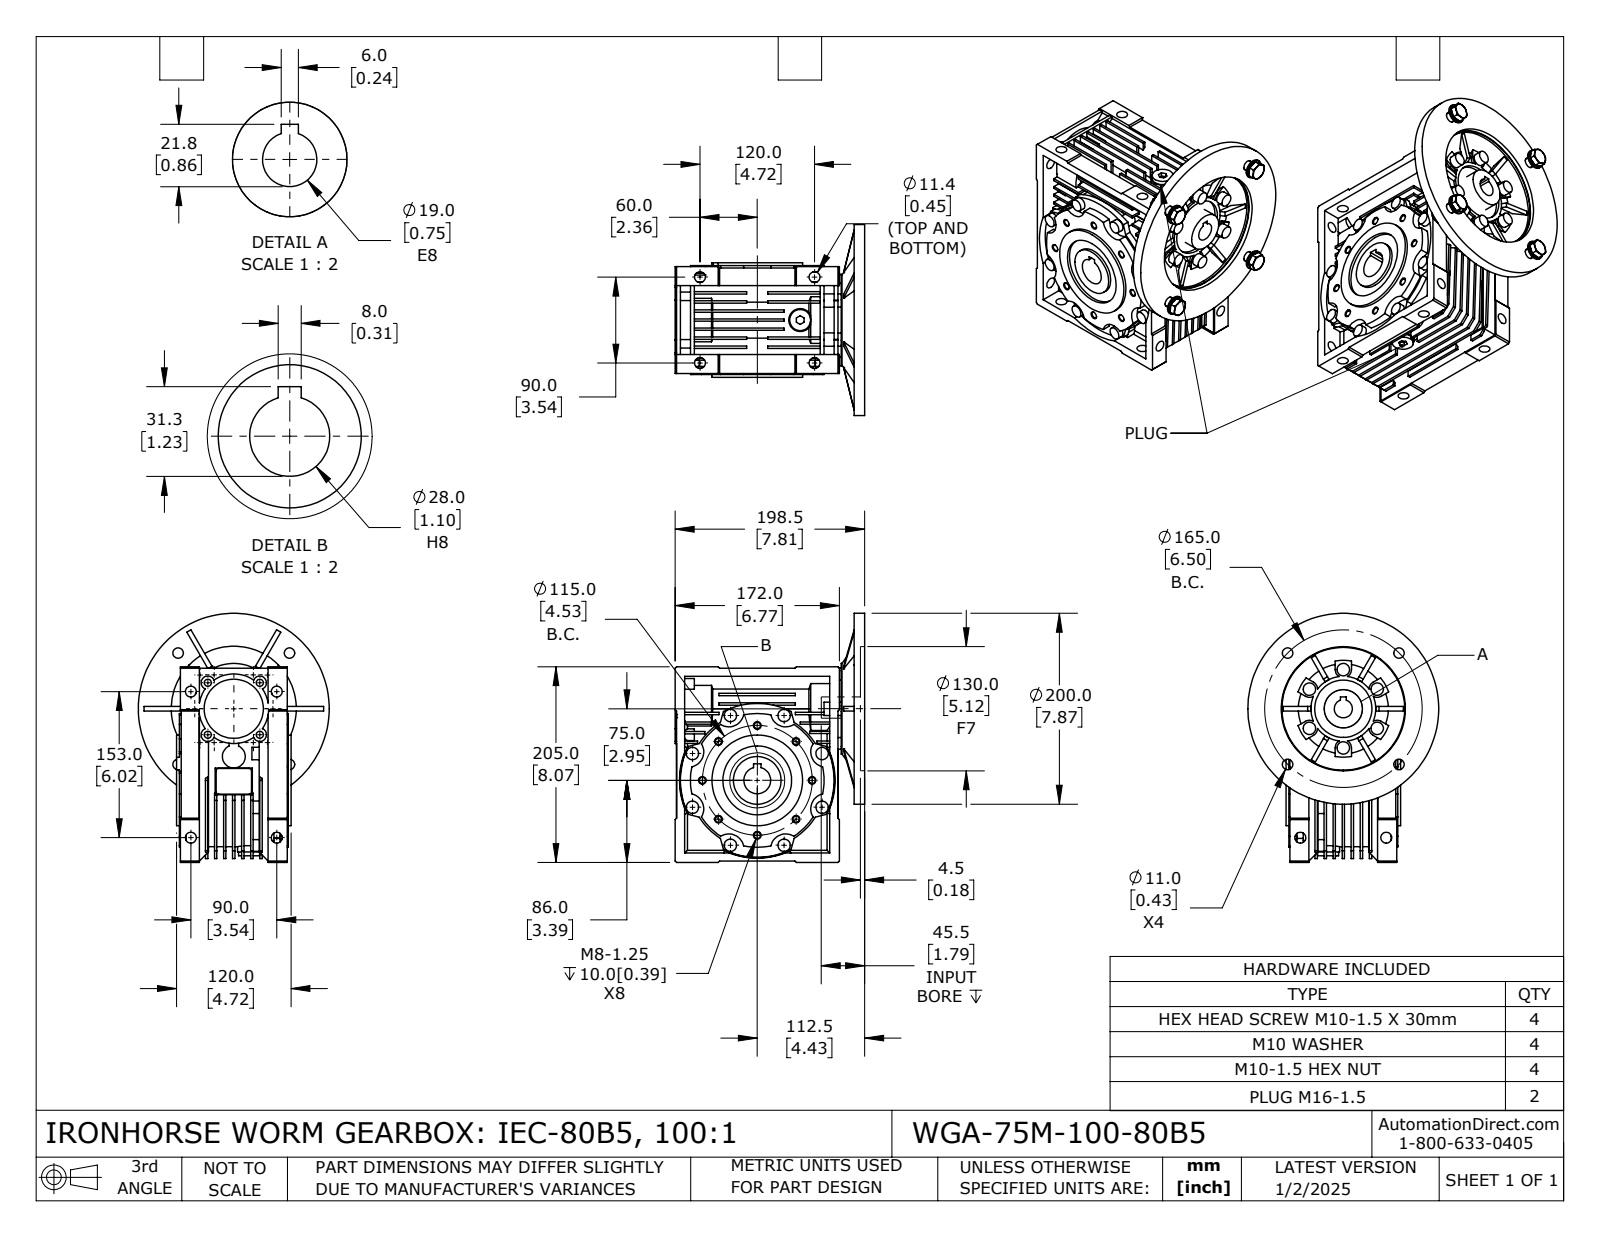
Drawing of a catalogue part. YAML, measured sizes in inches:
part_name: "WGA-75M-100-80B5"
step_written_by: "SolidWorks 2024 (CONFIG_CONTROL_DESIGN)"
units: inches
bodies: {solids: 20, faces: 1447, planar: 790, cylindrical: 439, other: 218}
overall_size: [10.276, 8.462, 7.874]
volume: 186.2
surface_area: 831.4
round_holes:
  - {diameter: 0.262, count: 8}
  - {diameter: 0.448, count: 8}
  - {diameter: 0.293, count: 4}
  - {diameter: 0.335, count: 4}
  - {diameter: 0.394, count: 4}
  - {diameter: 0.413, count: 4}
  - {diameter: 0.433, count: 4}
  - {diameter: 0.571, count: 2}
  - {diameter: 0.748, count: 1}
  - {diameter: 0.787, count: 1}
  - {diameter: 1.102, count: 1}
  - {diameter: 1.535, count: 1}
round_bosses_or_shafts:
  - {diameter: 0.512, count: 14}
  - {diameter: 0.787, count: 4}
  - {diameter: 0.63, count: 4}
  - {diameter: 0.945, count: 3}
  - {diameter: 3.74, count: 2}
  - {diameter: 0.866, count: 2}
  - {diameter: 0.622, count: 2}
  - {diameter: 0.539, count: 2}
partial_cylinders:
  - {radius: 0.276, count: 10}
  - {radius: 0.63, count: 8}
  - {radius: 0.335, count: 6}
  - {radius: 0.098, count: 4}
  - {radius: 1.338, count: 1}
  - {radius: 1.417, count: 1}
  - {radius: 1.437, count: 1}
  - {radius: 1.535, count: 1}
face_to_face_distances: [0.374, 0.098, 0.748, 0.472, 0.276, 1.122, 0.65, 0.394, 1.093, 0.846]
hole_center_spacings: [1.733, 2.264, 3.202, 3.584, 4.183, 1.515, 2.143, 3.248]
